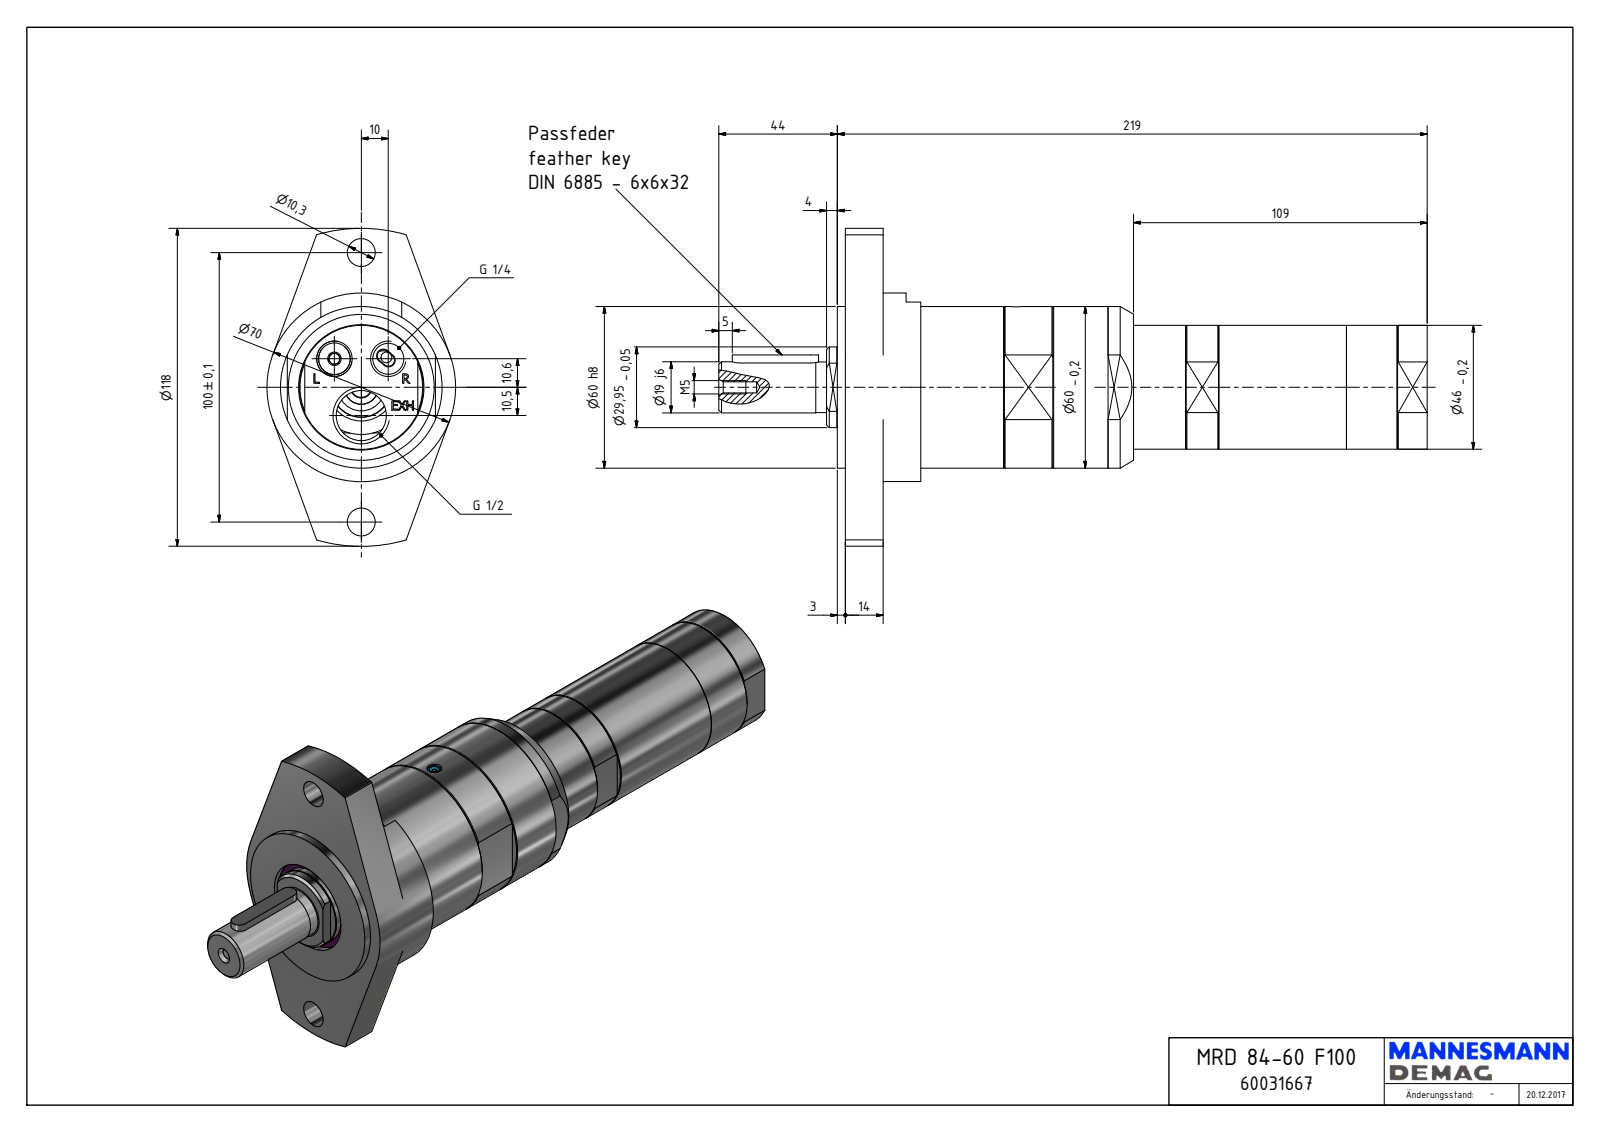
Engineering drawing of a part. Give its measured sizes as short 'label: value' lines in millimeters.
name: MRD 84-60 F100_60031667
written by: Autodesk Inventor 2018 (AUTOMOTIVE_DESIGN)
unit: mm
bodies: 1 solid, 226 faces (134 planar, 49 cylindrical, 43 other)
size: 263 × 118 × 70
volume: 554 315 mm³; area: 59 899 mm²
holes: 2× ⌀4, 2× ⌀10.3, 1× ⌀1.55, 1× ⌀4.13, 1× ⌀5.5, 1× ⌀11.45, 1× ⌀18.63, 1× ⌀35, 1× ⌀46.5
bosses: 1× ⌀70, 1× ⌀60, 1× ⌀55.18, 1× ⌀46, 1× ⌀29.95, 1× ⌀19, 1× ⌀18.8, 1× ⌀5
rounds: 2× R3, 2× R5, 1× R5.72, 1× R16.99, 1× R19, 1× R26.19, 1× R59
face distances: 14, 3, 17, 219, 216, 202, 31, 28, 188, 6.5
hole spacings: 14.57, 23.35, 40.65, 50, 61.42, 10.5, 20, 39.5
